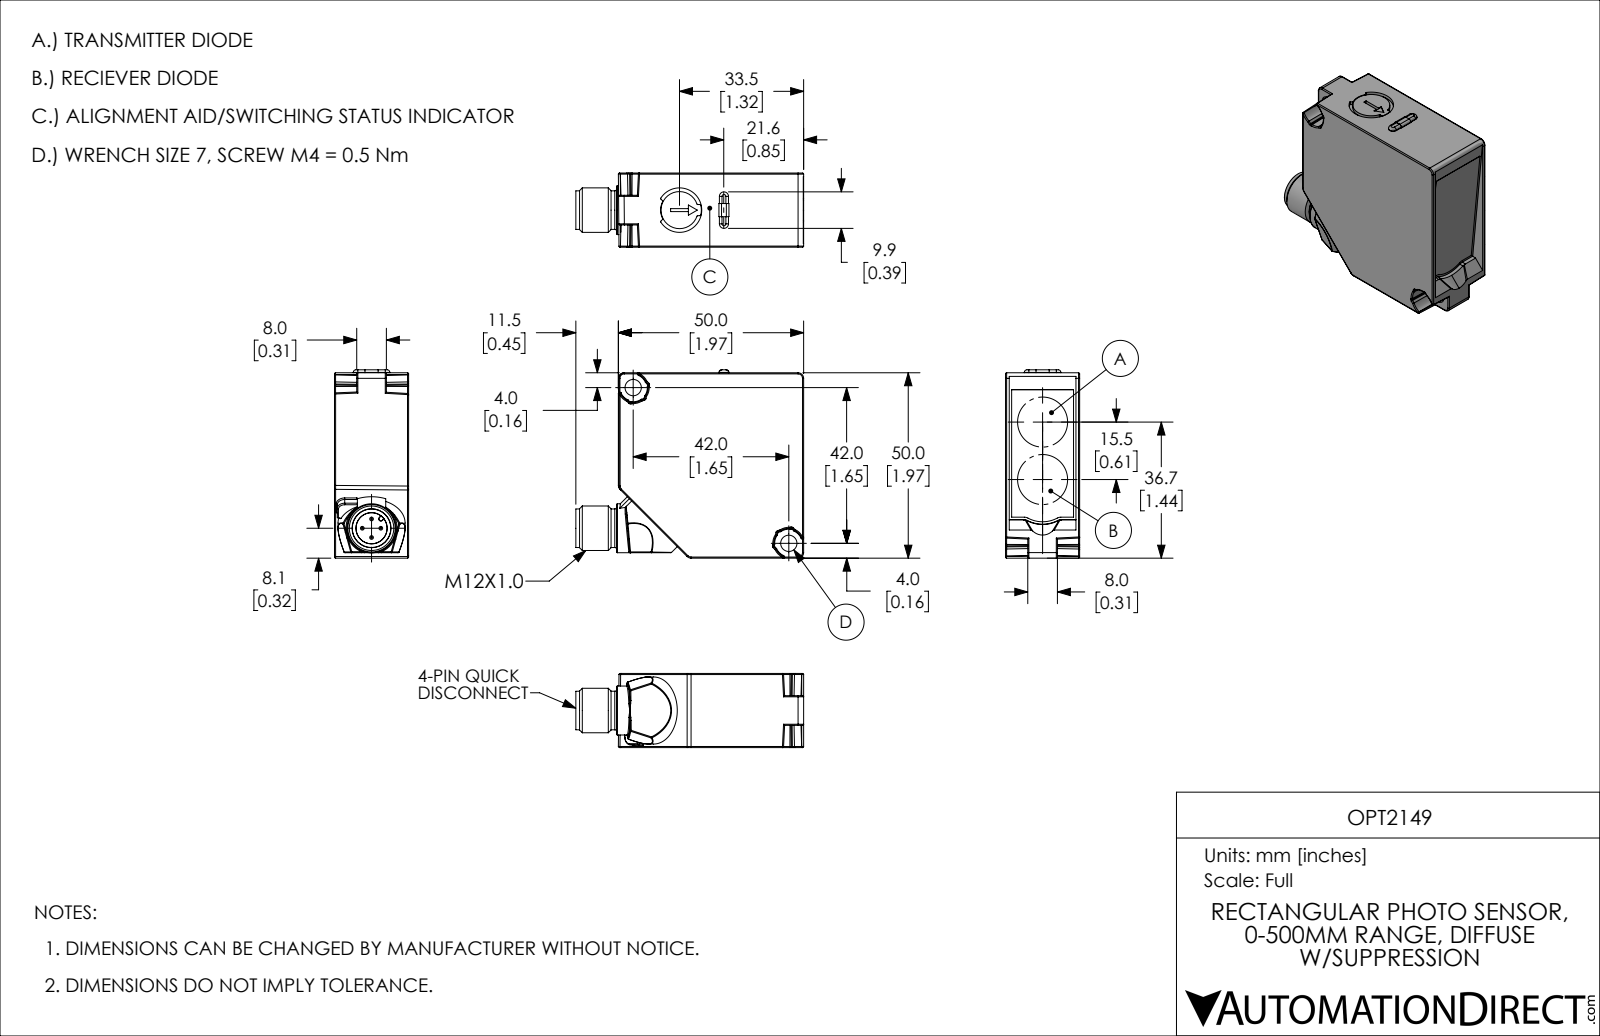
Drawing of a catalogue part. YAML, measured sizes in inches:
part_name: "OPT2149"
step_written_by: "SolidWorks 2019 (AUTOMOTIVE_DESIGN)"
units: inches
bodies: {solids: 1, faces: 342, planar: 109, cylindrical: 120, other: 113}
overall_size: [2.42, 2, 0.787]
volume: 2.813
surface_area: 15.65
round_holes:
  - {diameter: 0.173, count: 2}
  - {diameter: 0.472, count: 1}
  - {diameter: 0.713, count: 1}
round_bosses_or_shafts:
  - {diameter: 0.039, count: 4}
  - {diameter: 0.52, count: 1}
  - {diameter: 0.472, count: 1}
  - {diameter: 0.409, count: 1}
  - {diameter: 0.394, count: 1}
partial_cylinders:
  - {radius: 0.012, count: 64}
  - {radius: 0.008, count: 8}
  - {radius: 0.059, count: 5}
  - {radius: 0.079, count: 5}
  - {radius: 0.028, count: 4}
  - {radius: 0.048, count: 2}
  - {radius: 0.201, count: 1}
  - {radius: 0.232, count: 1}
face_to_face_distances: [0.787, 1.969, 0.039, 0.748, 0.236, 0.551, 0.197, 0.512, 0.058, 1.911]
hole_center_spacings: [2.339]
